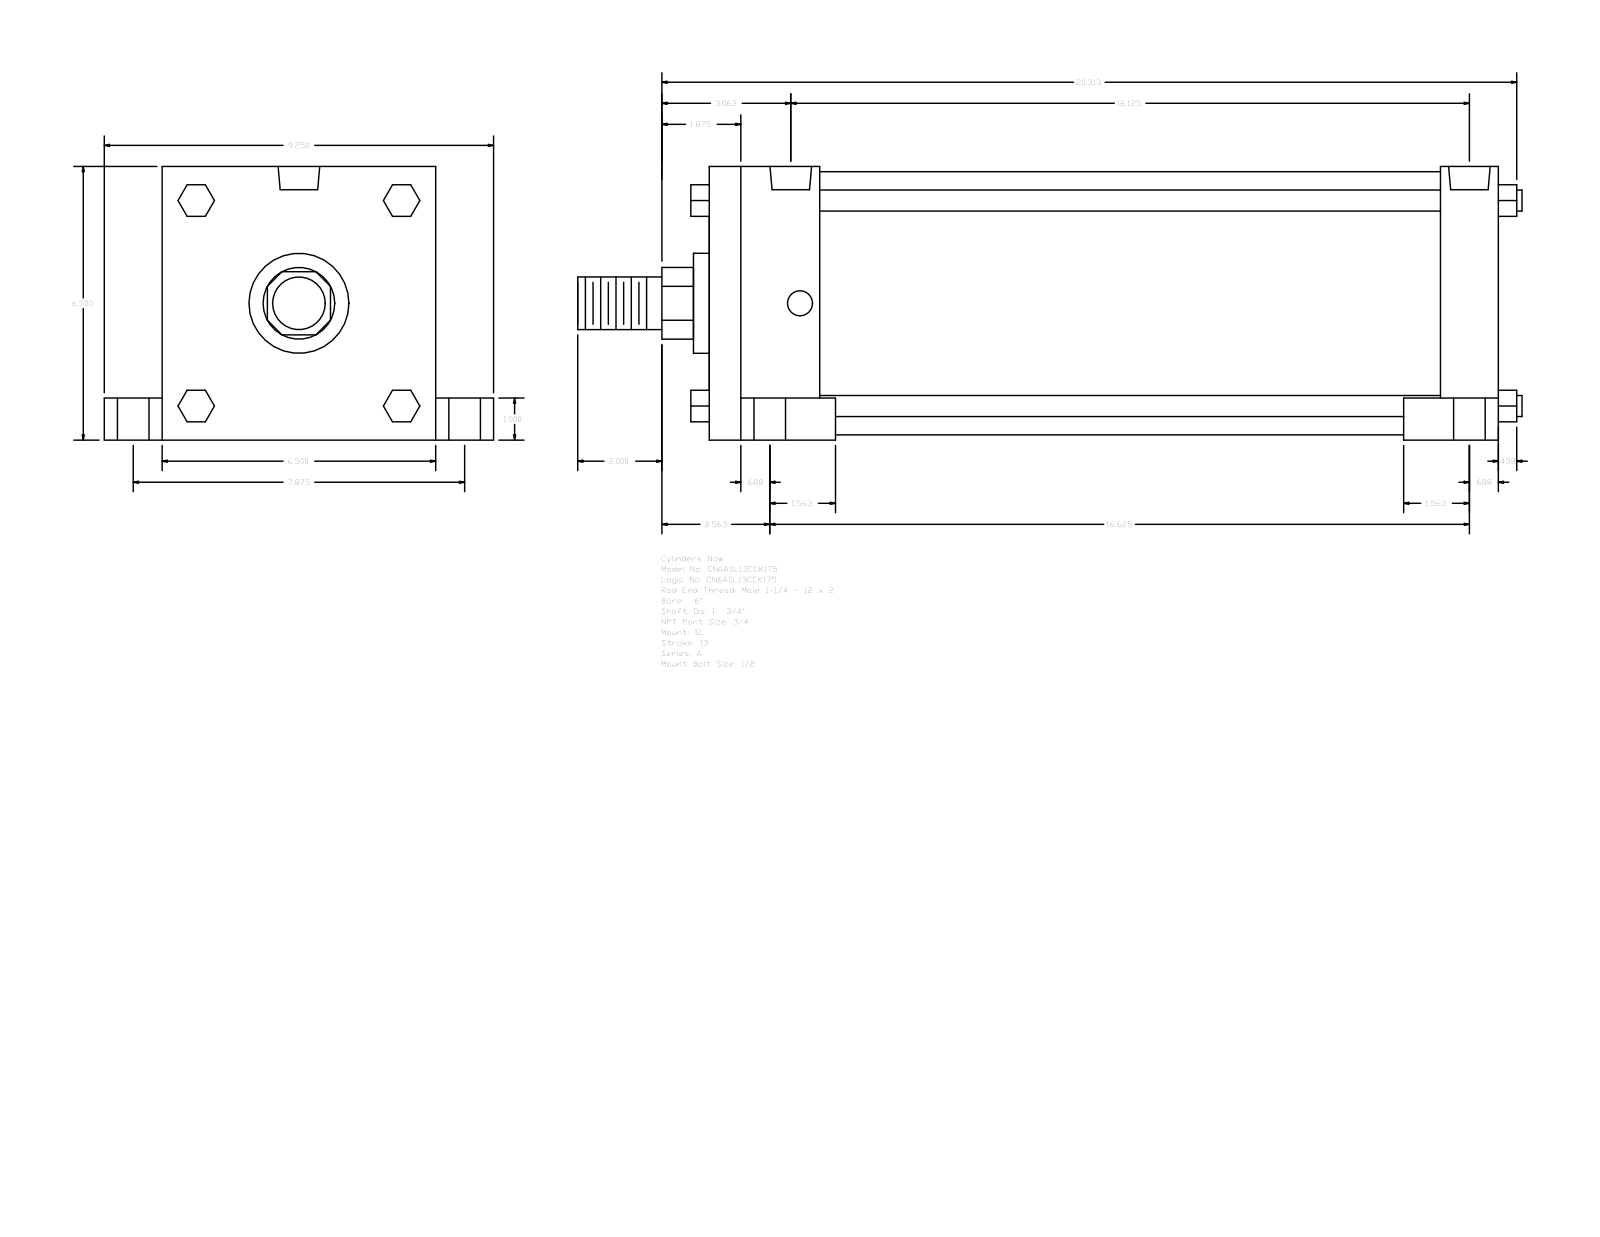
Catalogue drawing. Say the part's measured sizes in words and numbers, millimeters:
The part is named "A_SL__0600_1.75". Its 3-D file was written by "GSSL Pune (CONFIG_CONTROL_DESIGN)". It is 0 solids with 150 faces: 114 planar, 36 cylindrical and 0 other. Overall it measures 569.91 by 234.95 by 165.1 millimeters. Round holes: 4 of diameter 15.08, 4 of diameter 19.05, 4 of diameter 25.4, 2 of diameter 25.12. Round bosses or shafts: 4 of diameter 12.7, 1 of diameter 158.75, 1 of diameter 60.33, 1 of diameter 44.45, 1 of diameter 31.75. Partial cylindrical surfaces (rounded edges, fillets, slot ends): 1 of radius 21.63. The main face-to-face distances are 165.1, 476.25, 34.92, 66.68, 409.57, 441.33, 374.65, 25.4, 139.7, 200.02. The hole center spacings are 5.56, 100.01, 100.16, 100.81, 101.66, 200.02, 398.45, 404.01.
